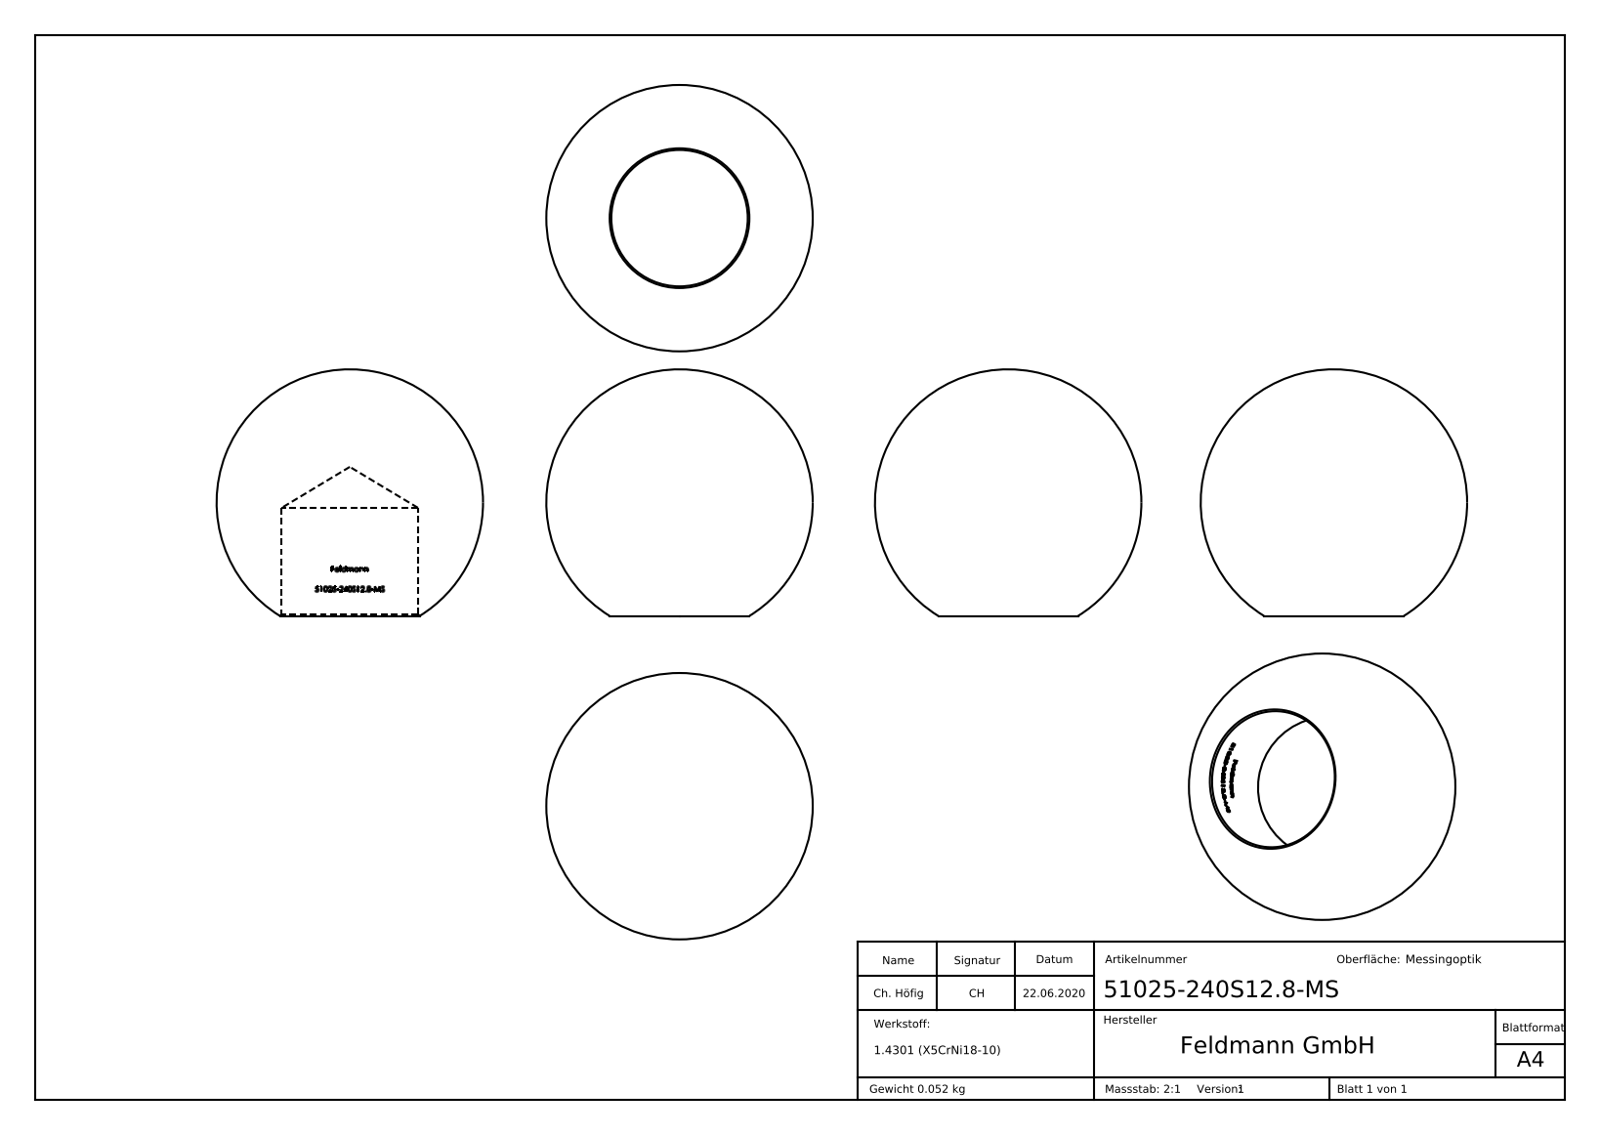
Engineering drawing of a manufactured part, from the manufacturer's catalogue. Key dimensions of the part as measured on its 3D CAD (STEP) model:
Part name (STEP PRODUCT): 51025-240S12.8-MS
STEP written by: SolidWorks 2015 (CONFIG_CONTROL_DESIGN)
Units: millimetres
Bodies: 1 solid, 322 faces (134 planar, 34 cylindrical, 154 other)
Overall size (bounding box): 25 × 25 × 23.14
Volume: 6 582 mm³ · Surface area: 2 384 mm²
Round holes (diameter × count): ⌀12.8 ×1
Partial cylindrical surfaces — rounded edges, fillets, slot ends (radius × count): R6.5 ×1
Main face-to-face distances: 1.83, 0.53, 2.29, 1.88, 1.35, 0.58, 1.19, 1.67, 1.74, 1.72
